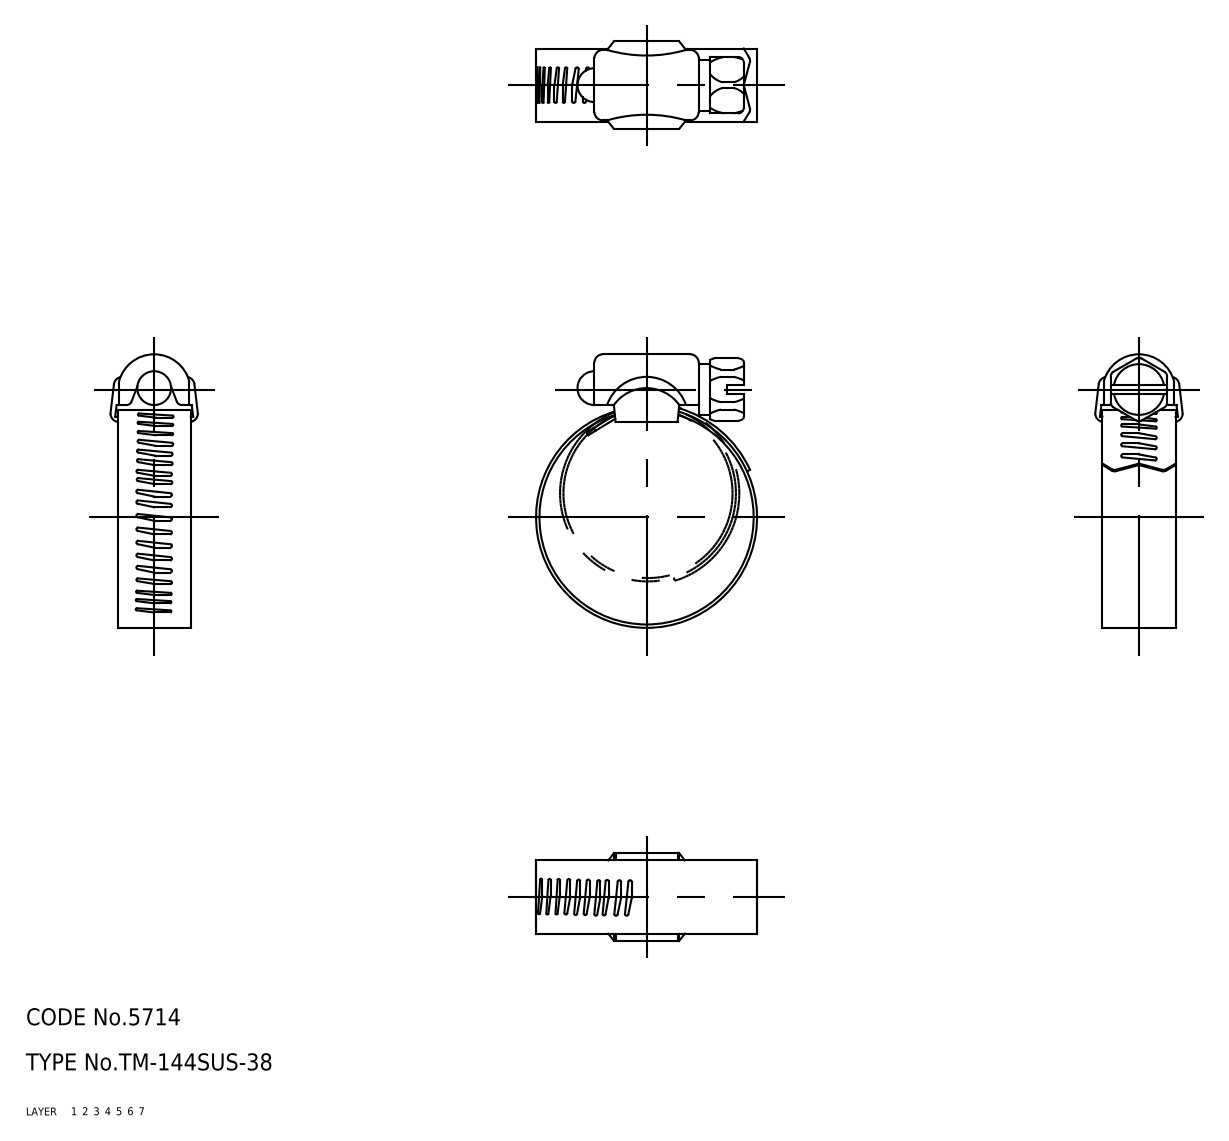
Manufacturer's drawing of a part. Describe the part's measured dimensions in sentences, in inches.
The part is named "screw; holder; band; TM_144SUS_38_20622_36". Its 3-D file was written by "CADfix (AUTOMOTIVE_DESIGN)". It is 3 solids with 228 faces: 0 planar, 0 cylindrical and 228 other. Overall it measures 1.913 by 1.543 by 0.615 inches. Its volume is 0.207 cubic inches and its surface area 9.906 square inches.
